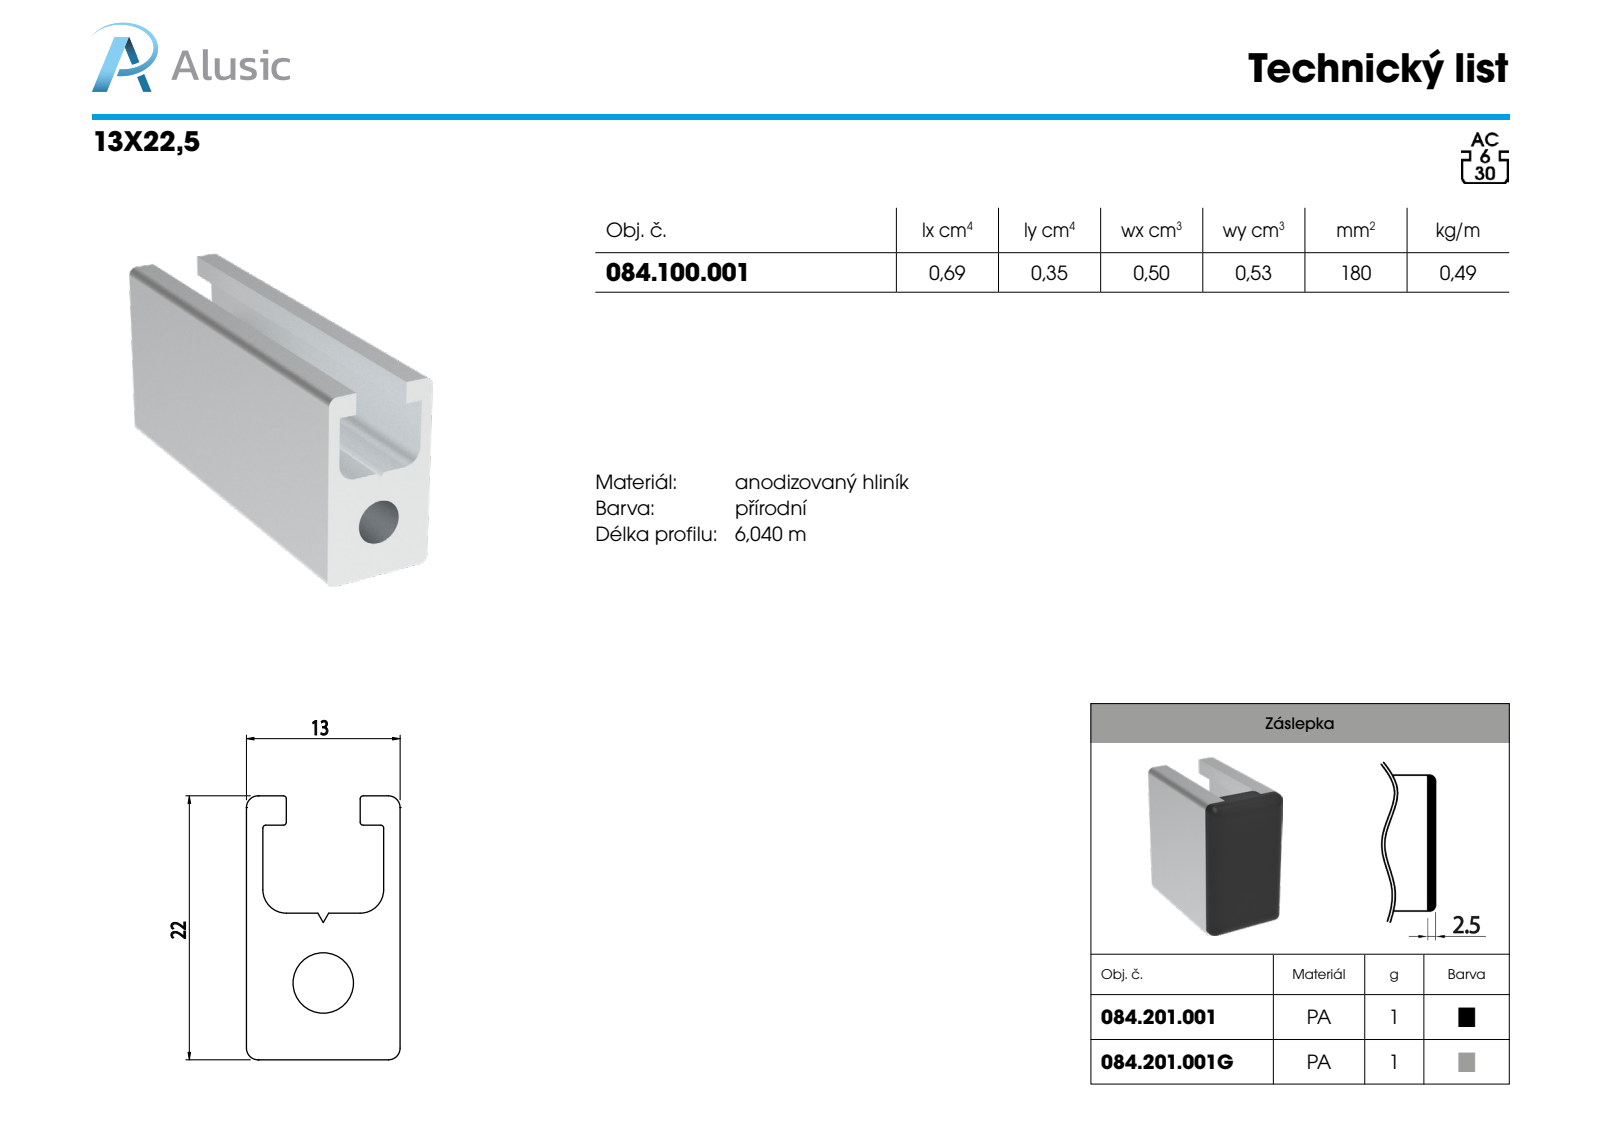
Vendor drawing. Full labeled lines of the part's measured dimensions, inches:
Part name (STEP PRODUCT): 084.201.001
STEP written by: SolidWorks 2011 (CONFIG_CONTROL_DESIGN)
Units: inches
Bodies: 1 solid, 30 faces (12 planar, 12 cylindrical, 6 other)
Overall size (bounding box): 0.866 × 0.512 × 0.256
Volume: 0.045 in³ · Surface area: 1.26 in²
Round holes (diameter × count): ⌀0.118 ×1
Round bosses / shafts (diameter × count): ⌀0.197 ×1
Partial cylindrical surfaces — rounded edges, fillets, slot ends (radius × count): R0.039 ×4, R0.079 ×4
Main face-to-face distances: 0.098, 0.079, 0.177, 0.091, 0.512, 0.138, 0.374, 0.866, 0.776, 0.256
